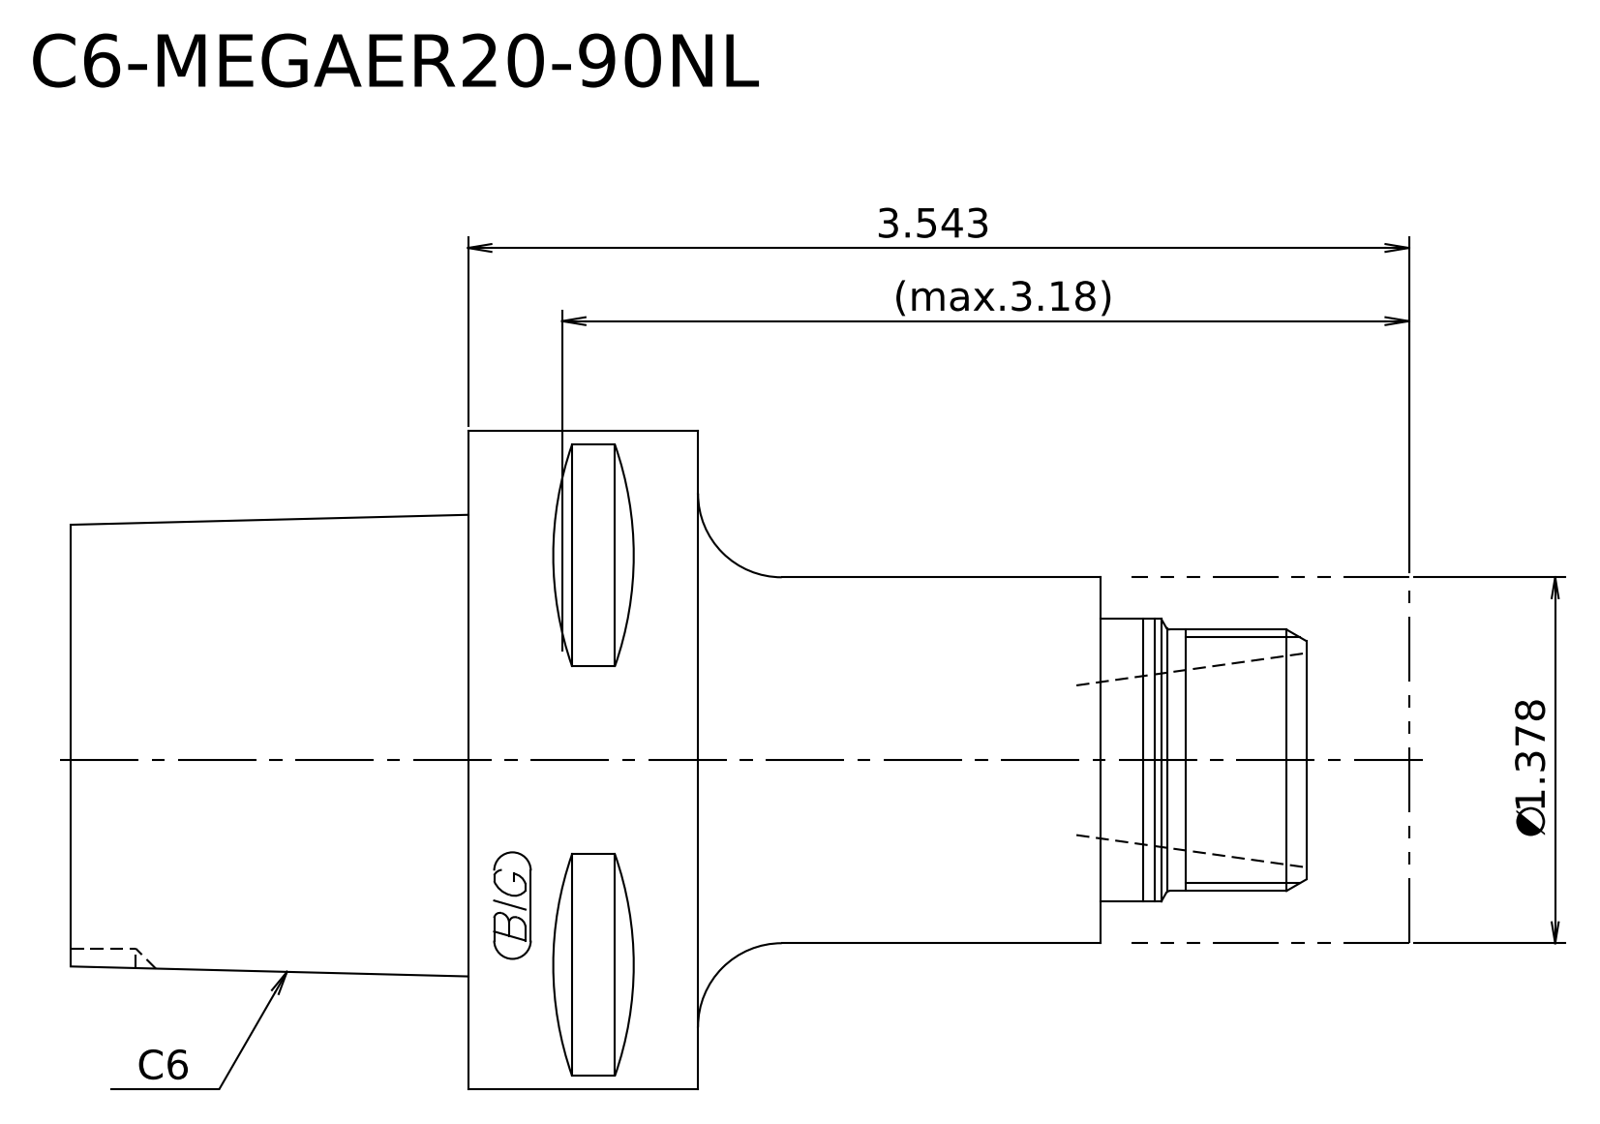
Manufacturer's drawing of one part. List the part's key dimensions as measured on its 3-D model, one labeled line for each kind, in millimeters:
STEP written by: Kubotek KeyCreator 2011 V10.0.2 (22737) (automotive_design)
Units: millimetres
Bodies: 2 solids, 18 faces (7 planar, 5 cylindrical, 6 other)
Overall size (bounding box): 128 × 63 × 63
Volume: 200 036 mm³ · Surface area: 25 741 mm²
Round bosses / shafts (diameter × count): ⌀63 ×1, ⌀35 ×1, ⌀27 ×1, ⌀25 ×1
Main face-to-face distances: 38, 22, 60, 41.5, 63.5, 101.5, 26.5, 68, 90, 128
